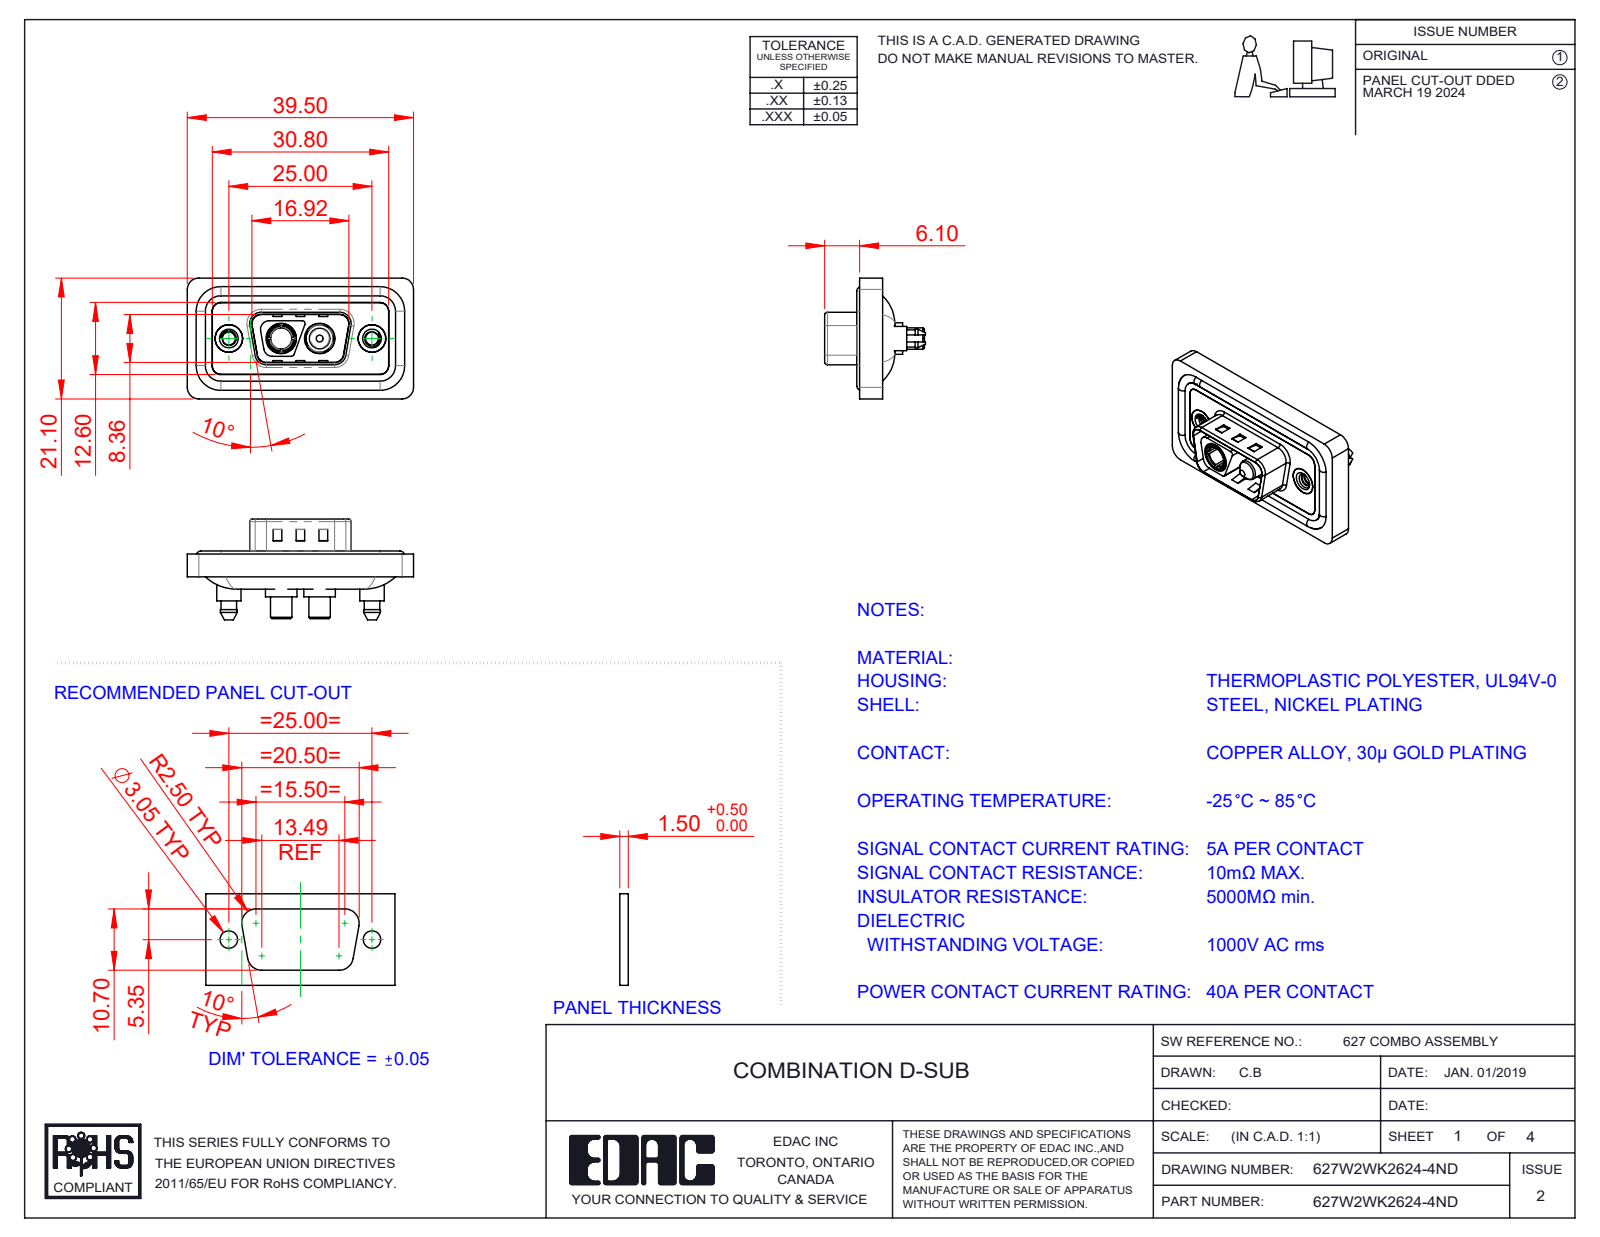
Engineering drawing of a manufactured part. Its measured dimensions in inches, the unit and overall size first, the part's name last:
Units: inches
Overall size (bounding box): 1.555 × 0.831 × 0.693
Round holes (diameter × count): ⌀0.089 ×2, ⌀0.157 ×2, ⌀0.189 ×2, ⌀0.191 ×2, ⌀0.197 ×2, ⌀0.209 ×2, ⌀0.146 ×1
Round bosses / shafts (diameter × count): ⌀0.063 ×4, ⌀0.217 ×2, ⌀0.213 ×2, ⌀0.205 ×2, ⌀0.193 ×2, ⌀0.187 ×2, ⌀0.167 ×2, ⌀0.148 ×2
Partial cylindrical surfaces — rounded edges, fillets, slot ends (radius × count): R0.059 ×26, R0.079 ×18, R0.02 ×10, R0.063 ×10, R0.01 ×4, R0.024 ×4, R0.026 ×4, R0.035 ×4
Main face-to-face distances: 0.016, 0.043, 0.114, 0.122, 0.02, 0.063, 0.059, 0.157, 0.071, 0.126
Hole centre spacings: 0.36, 0.624, 0.265, 0.984
Volume: 0.288 in³ · Surface area: 11.94 in²
Bodies: 11 solids, 592 faces (205 planar, 267 cylindrical, 120 other)
Part name (STEP PRODUCT): 627Combo Waterproof Housing_09 Contacts; 627Combo Shell Rear_09 Contacts; Power Pin_40A S; 627Combo Threaded Boardlock_5 (+5 more)
STEP written by: SolidWorks 2023 (CONFIG_CONTROL_DESIGN)
